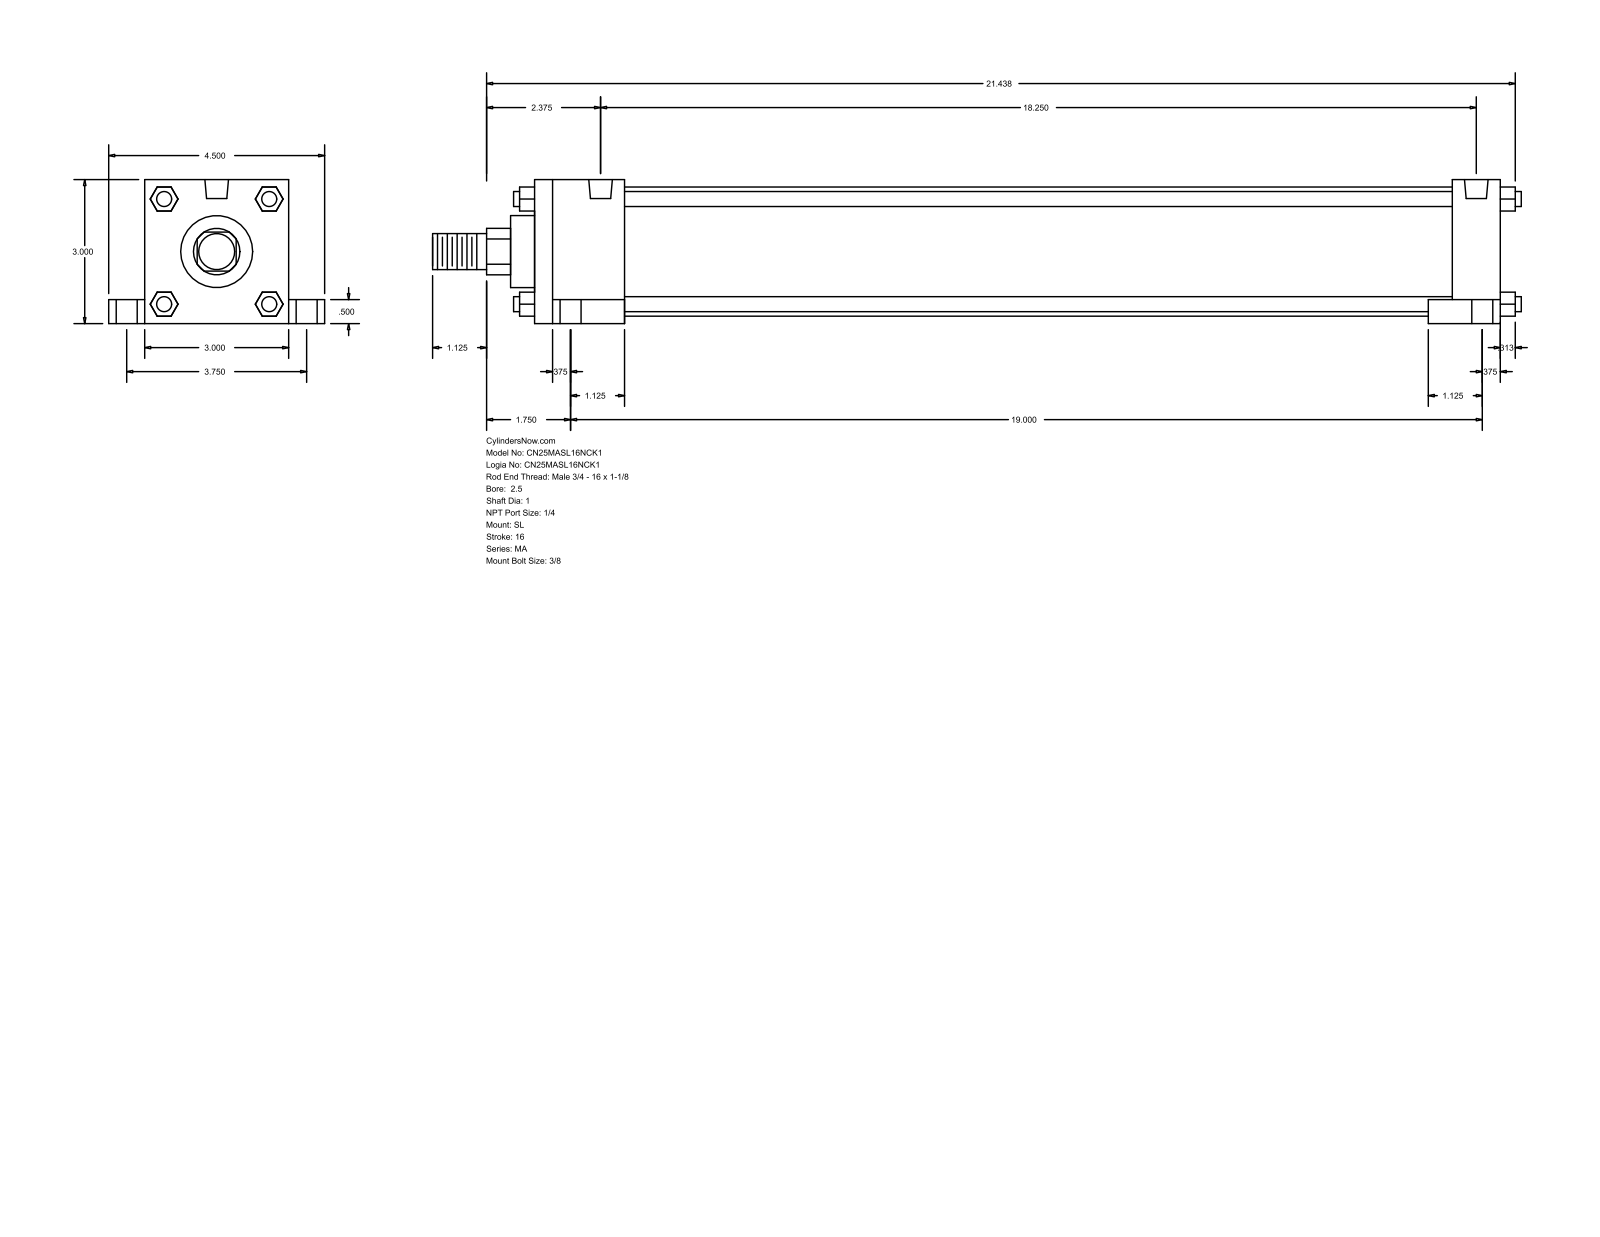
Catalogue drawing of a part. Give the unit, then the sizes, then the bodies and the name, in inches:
Units: inches
Overall size (bounding box): 22.687 × 4.5 × 3
Round holes (diameter × count): ⌀0.313 ×4, ⌀0.437 ×4, ⌀0.687 ×4, ⌀0.492 ×2
Round bosses / shafts (diameter × count): ⌀0.313 ×4, ⌀2.69 ×1, ⌀1.5 ×1, ⌀1 ×1, ⌀0.75 ×1
Partial cylindrical surfaces — rounded edges, fillets, slot ends (radius × count): R0.484 ×1
Main face-to-face distances: 3, 20.125, 0.5, 17.25, 1, 1.875, 18.25, 19.125, 0.75, 3.75
Hole centre spacings: 1.879, 1.976, 3.75, 18.25, 18.47, 18.968, 19, 19.367
Bodies: 0 solids, 148 faces (112 planar, 36 cylindrical, 0 other)
Part name (STEP PRODUCT): MA_SL__0250_1
STEP written by: GSSL Pune (CONFIG_CONTROL_DESIGN)
